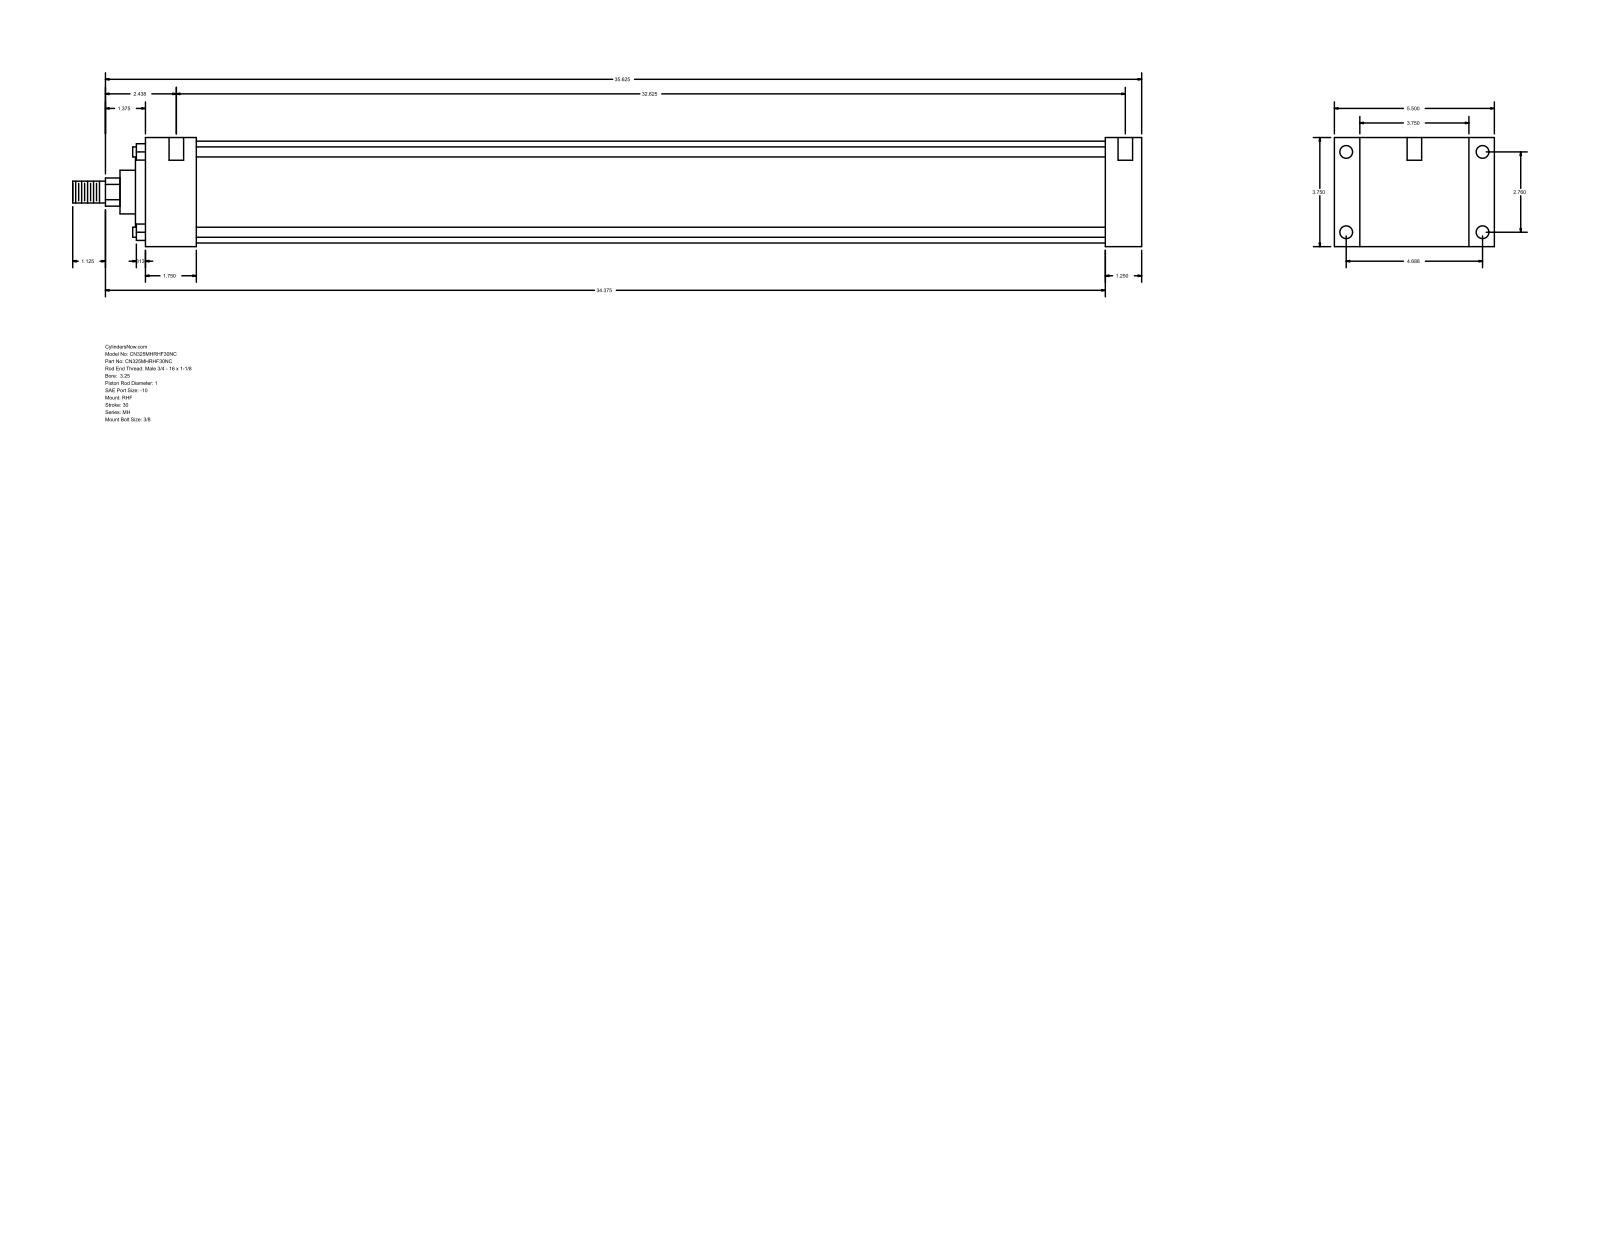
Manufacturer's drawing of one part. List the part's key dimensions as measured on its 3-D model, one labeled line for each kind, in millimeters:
Part name (STEP PRODUCT): MH_RHF__0325_1
STEP written by: GSSL Pune (CONFIG_CONTROL_DESIGN)
Units: millimetres
Bodies: 0 solids, 90 faces (61 planar, 29 cylindrical, 0 other)
Overall size (bounding box): 933.45 × 139.7 × 95.25
Round holes (diameter × count): ⌀5.56 ×4, ⌀11.13 ×4, ⌀12.7 ×2
Round bosses / shafts (diameter × count): ⌀8.76 ×4, ⌀88.9 ×1, ⌀60.33 ×1, ⌀38.1 ×1, ⌀25.4 ×1, ⌀19.05 ×1
Partial cylindrical surfaces — rounded edges, fillets, slot ends (radius × count): R12.29 ×1
Main face-to-face distances: 95.24, 31.76, 22.23, 117.47, 838.2, 869.96, 139.7, 44.46, 793.74, 825.5
Hole centre spacings: 70.1, 119.06, 138.16, 835.02, 1.58, 4.76, 828.68, 830.26
